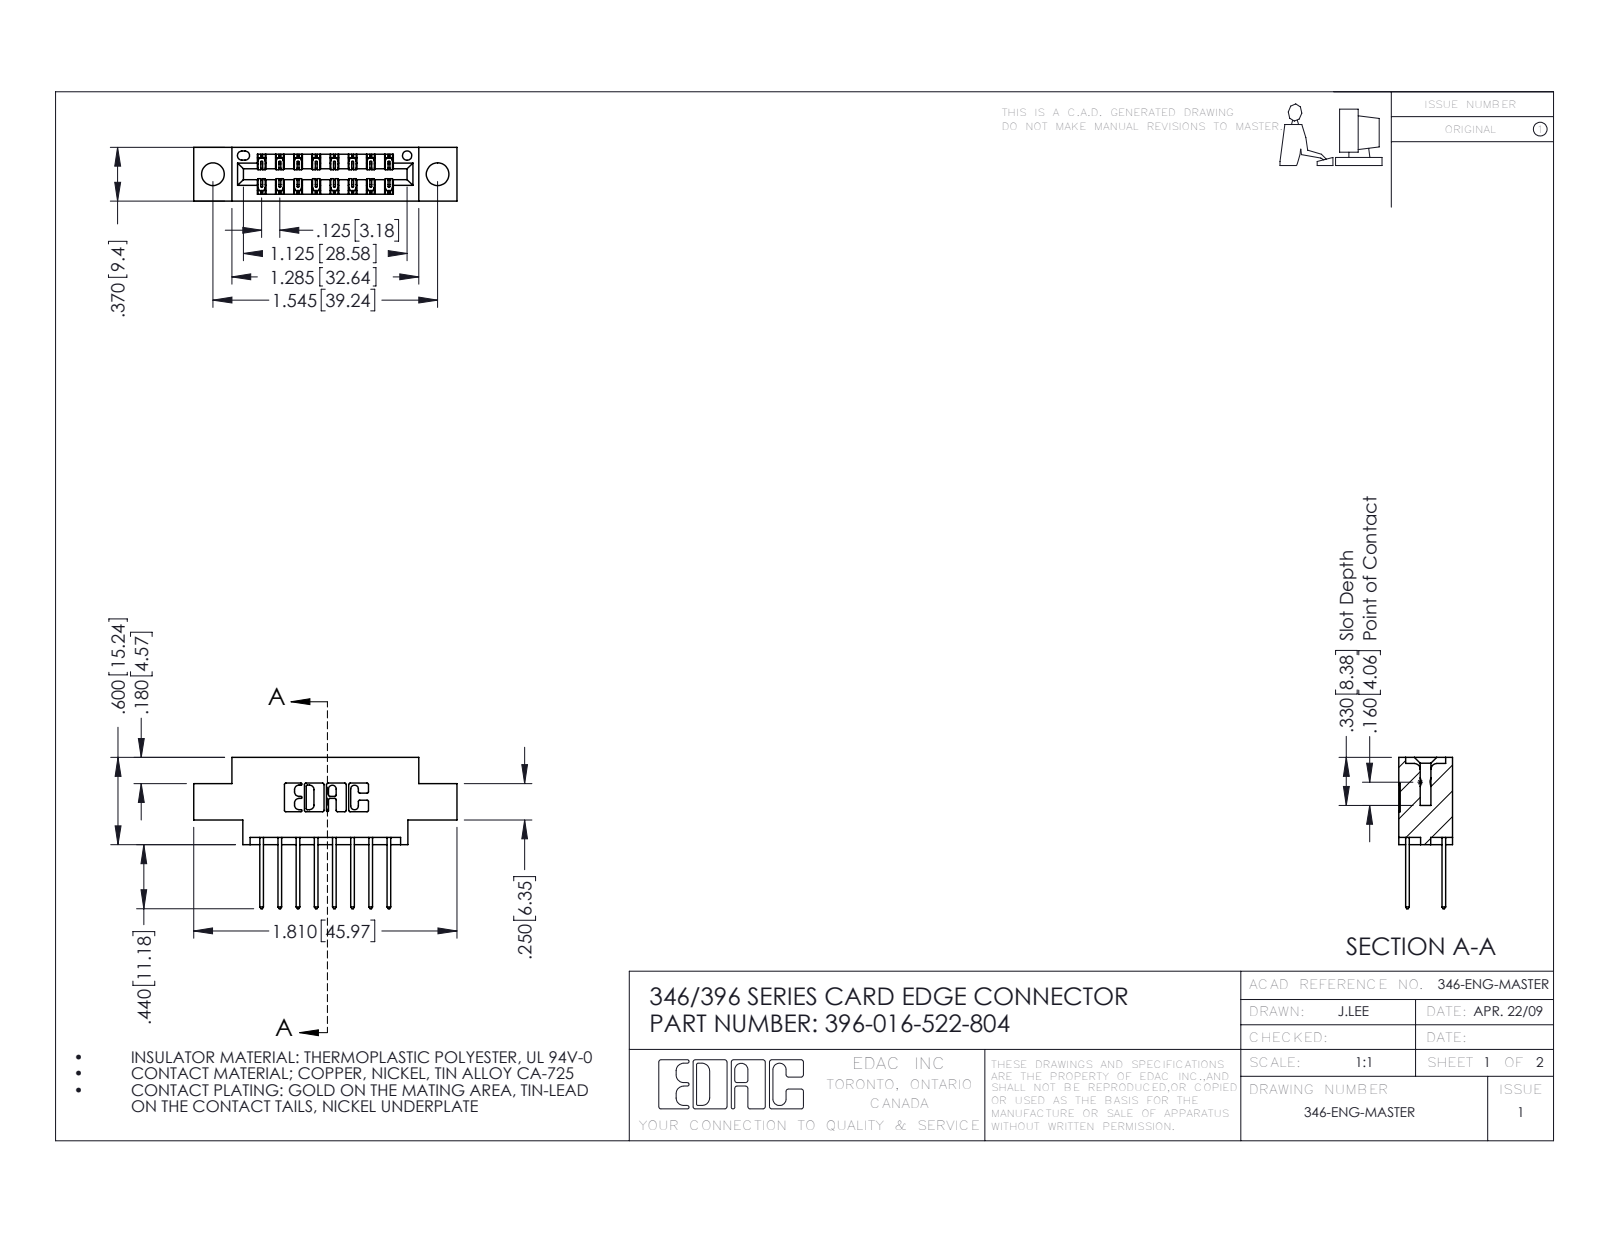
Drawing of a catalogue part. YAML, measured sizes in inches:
part_name: "396-016-522-804; 346 Part_0.170 Offset - 0.156 Dia-TH; 345-292-001_345-293-122"
step_written_by: "SolidWorks 2016 (CONFIG_CONTROL_DESIGN)"
units: inches
bodies: {solids: 17, faces: 958, planar: 640, cylindrical: 318, other: 0}
overall_size: [1.81, 1.04, 0.37]
volume: 0.245
surface_area: 8.015
round_holes:
  - {diameter: 0.156, count: 2}
  - {diameter: 0.064, count: 1}
partial_cylinders:
  - {radius: 0.006, count: 24}
  - {radius: 0.01, count: 22}
  - {radius: 0.01, count: 16}
  - {radius: 0.007, count: 6}
  - {radius: 0.031, count: 6}
  - {radius: 0.026, count: 3}
  - {radius: 0.014, count: 2}
  - {radius: 0.022, count: 2}
face_to_face_distances: [0.25, 0.048, 0.322, 0.37, 0.072, 0.298, 0.025, 0.275, 0.148, 0.222]
hole_center_spacings: [0.246, 1.341, 1.545]
